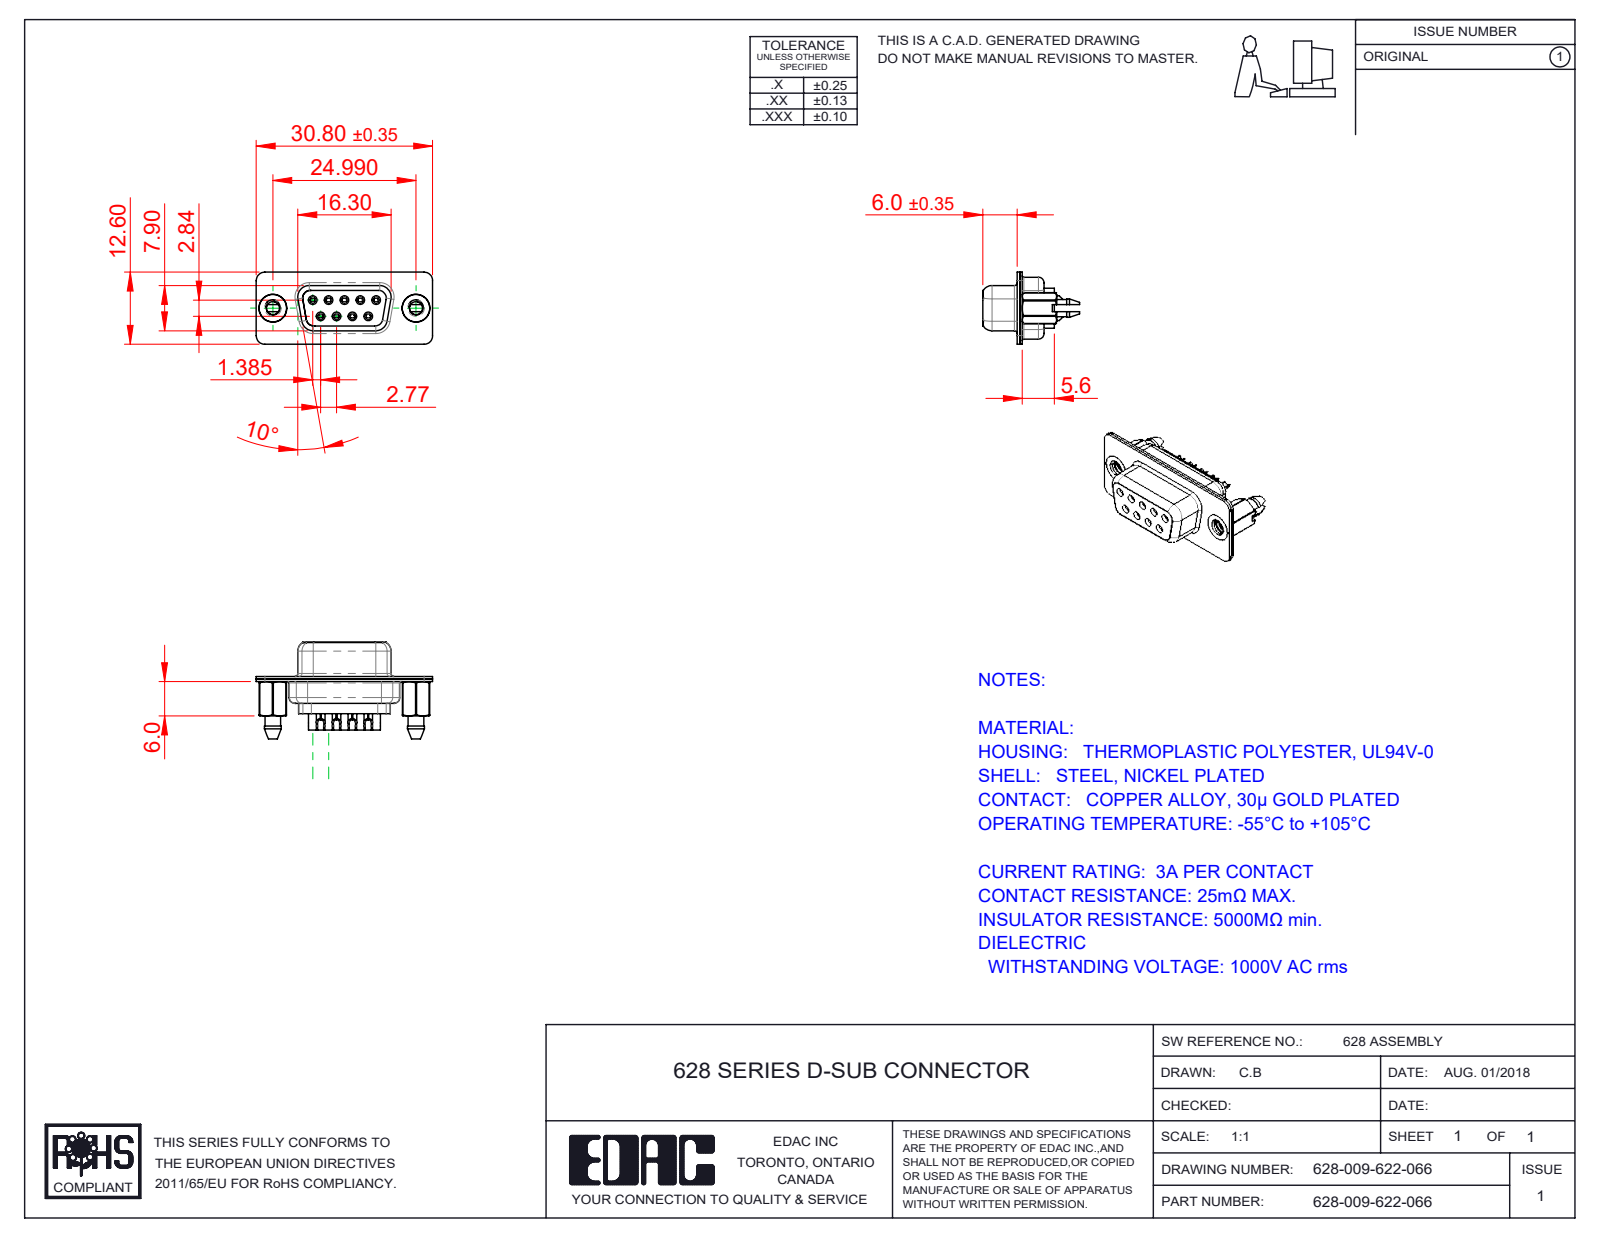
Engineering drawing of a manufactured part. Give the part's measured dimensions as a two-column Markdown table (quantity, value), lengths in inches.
| quantity | value |
| --- | --- |
| part name | 628 4-40 Threaded Boardlock_LP; 628 Contact Row 1_22L; 628 Housing_09 LP; 628-009-622-066 (+3 more) |
| STEP written by | SolidWorks 2020 (CONFIG_CONTROL_DESIGN) |
| units | inches |
| bodies | 14 solids, 1154 faces (288 planar, 394 cylindrical, 472 other) |
| overall size | 1.213 × 0.665 × 0.496 |
| volume | 0.114 in³ |
| surface area | 7.465 in² |
| round holes (diameter × count) | 0.031 × 9, 0.035 × 9, 0.043 × 9, 0.063 × 9, 0.067 × 5, 0.089 × 2, 0.157 × 2, 0.159 × 2, 0.191 × 2 |
| round bosses / shafts (diameter × count) | 0.079 × 9, 0.059 × 9, 0.047 × 9, 0.195 × 2, 0.189 × 2 |
| partial cylindrical surfaces (radius × count) | 0.059 × 19, 0.079 × 12, 0.011 × 9, 0.039 × 6, 0.053 × 6, 0.063 × 6, 0.01 × 4, 0.02 × 4 |
| main face-to-face distances | 0.018, 0.016, 0.035, 0.075, 0.335, 0.26, 0.055, 0.02, 0.256, 0.492 |
| hole center spacings | 0.124, 0.109, 0.218, 0.198, 0.198, 0.327, 0.294, 0.295 |
